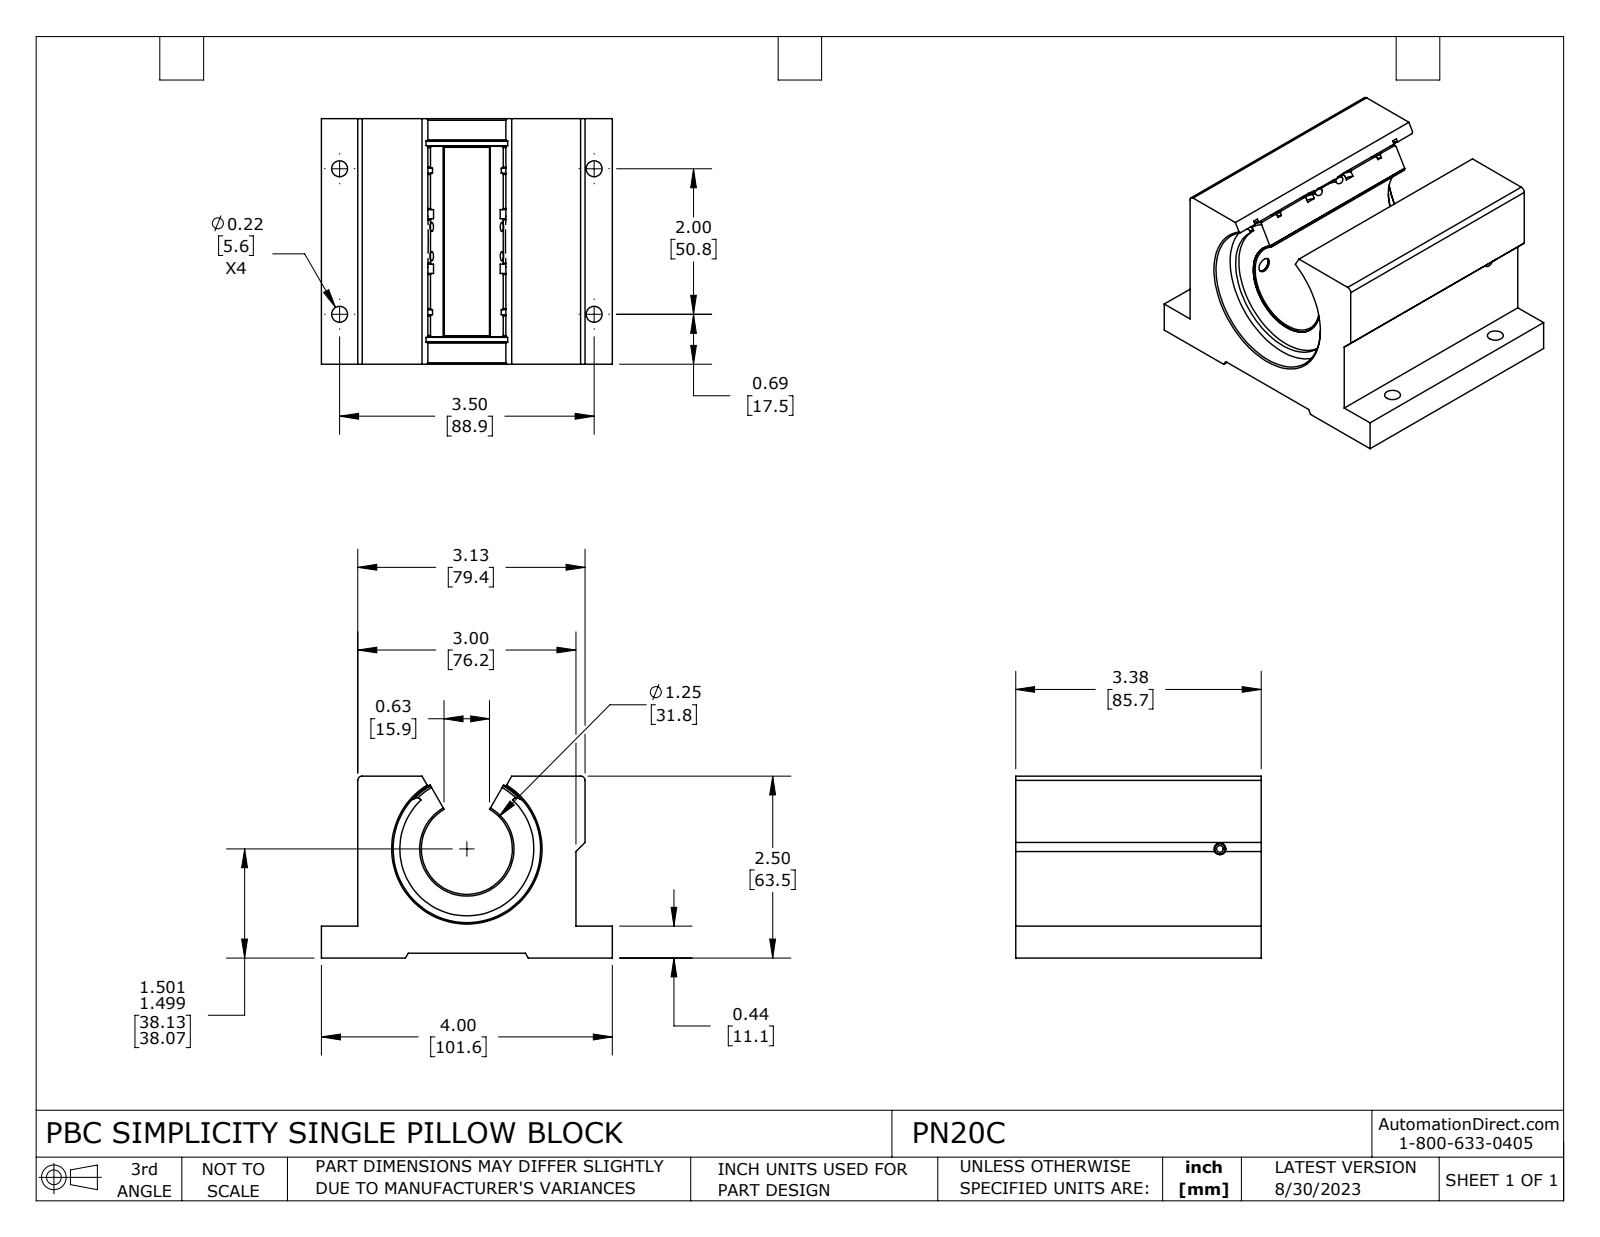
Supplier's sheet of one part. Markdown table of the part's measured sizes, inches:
| quantity | value |
| --- | --- |
| part name | PN20C |
| STEP written by | SolidWorks 2021 (CONFIG_CONTROL_DESIGN) |
| units | inches |
| bodies | 8 solids, 203 faces (53 planar, 94 cylindrical, 56 other) |
| overall size | 4 × 3.375 × 2.5 |
| volume | 19.89 in³ |
| surface area | 126 in² |
| round holes (diameter × count) | 0.219 × 4, 0.092 × 1, 0.157 × 1, 0.201 × 1, 1.252 × 1, 1.295 × 1, 2.028 × 1, 2.122 × 1 |
| round bosses / shafts (diameter × count) | 1.999 × 1, 1.889 × 1, 1.838 × 1, 0.156 × 1 |
| partial cylindrical surfaces (radius × count) | 0.05 × 2, 0.06 × 2, 0.18 × 2, 0.921 × 1, 1.077 × 1 |
| main face-to-face distances | 2.5, 0.065, 2.435, 3.375, 3, 0.437, 0.372, 2.063, 0.379, 0.5 |
| hole center spacings | 2, 3.5, 4.031, 2.243 |
